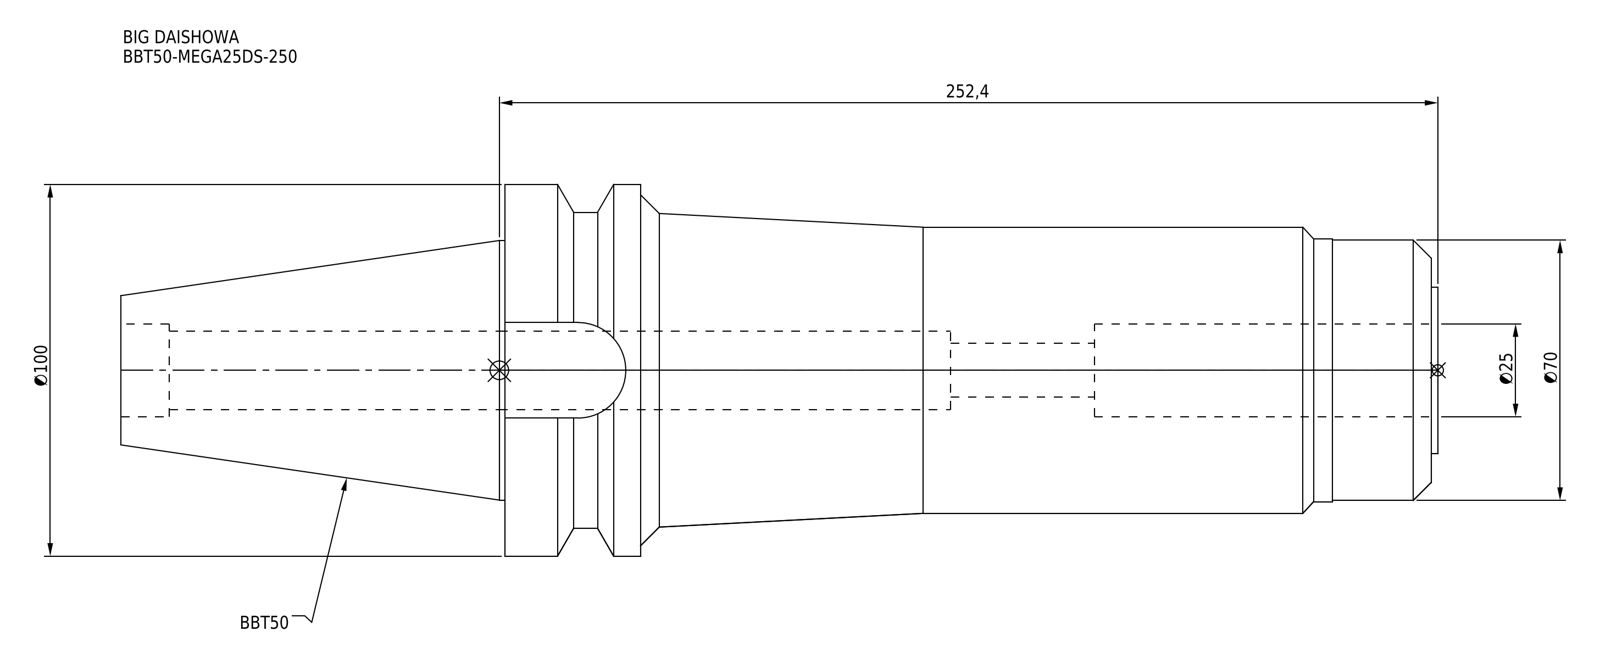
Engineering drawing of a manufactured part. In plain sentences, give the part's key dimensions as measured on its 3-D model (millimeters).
The part is named "BBT50-MEGA25DS-250". Its 3-D file was written by "CREO PARAMETRIC BY PTC INC, 2016380 (AUTOMOTIVE_DESIGN)". It is 1 solid with 57 faces: 15 planar, 28 cylindrical and 14 other. Overall it measures 354.2 by 100 by 100 millimeters. Its volume is 1 372 000 cubic millimeters and its surface area 118 256 square millimeters. Round holes: 1 of diameter 14.5, 1 of diameter 21.2, 1 of diameter 25. Round bosses or shafts: 1 of diameter 100, 1 of diameter 85, 1 of diameter 77, 1 of diameter 70.7, 1 of diameter 70, 1 of diameter 69.85, 1 of diameter 44.8. Partial cylindrical surfaces (rounded edges, fillets, slot ends): 1 of radius 12.85. The main face-to-face distances are 249.1, 1.8, 250.9, 214.4, 212.6, 36.5, 354.2, 352.4, 139.8, 103.3.
